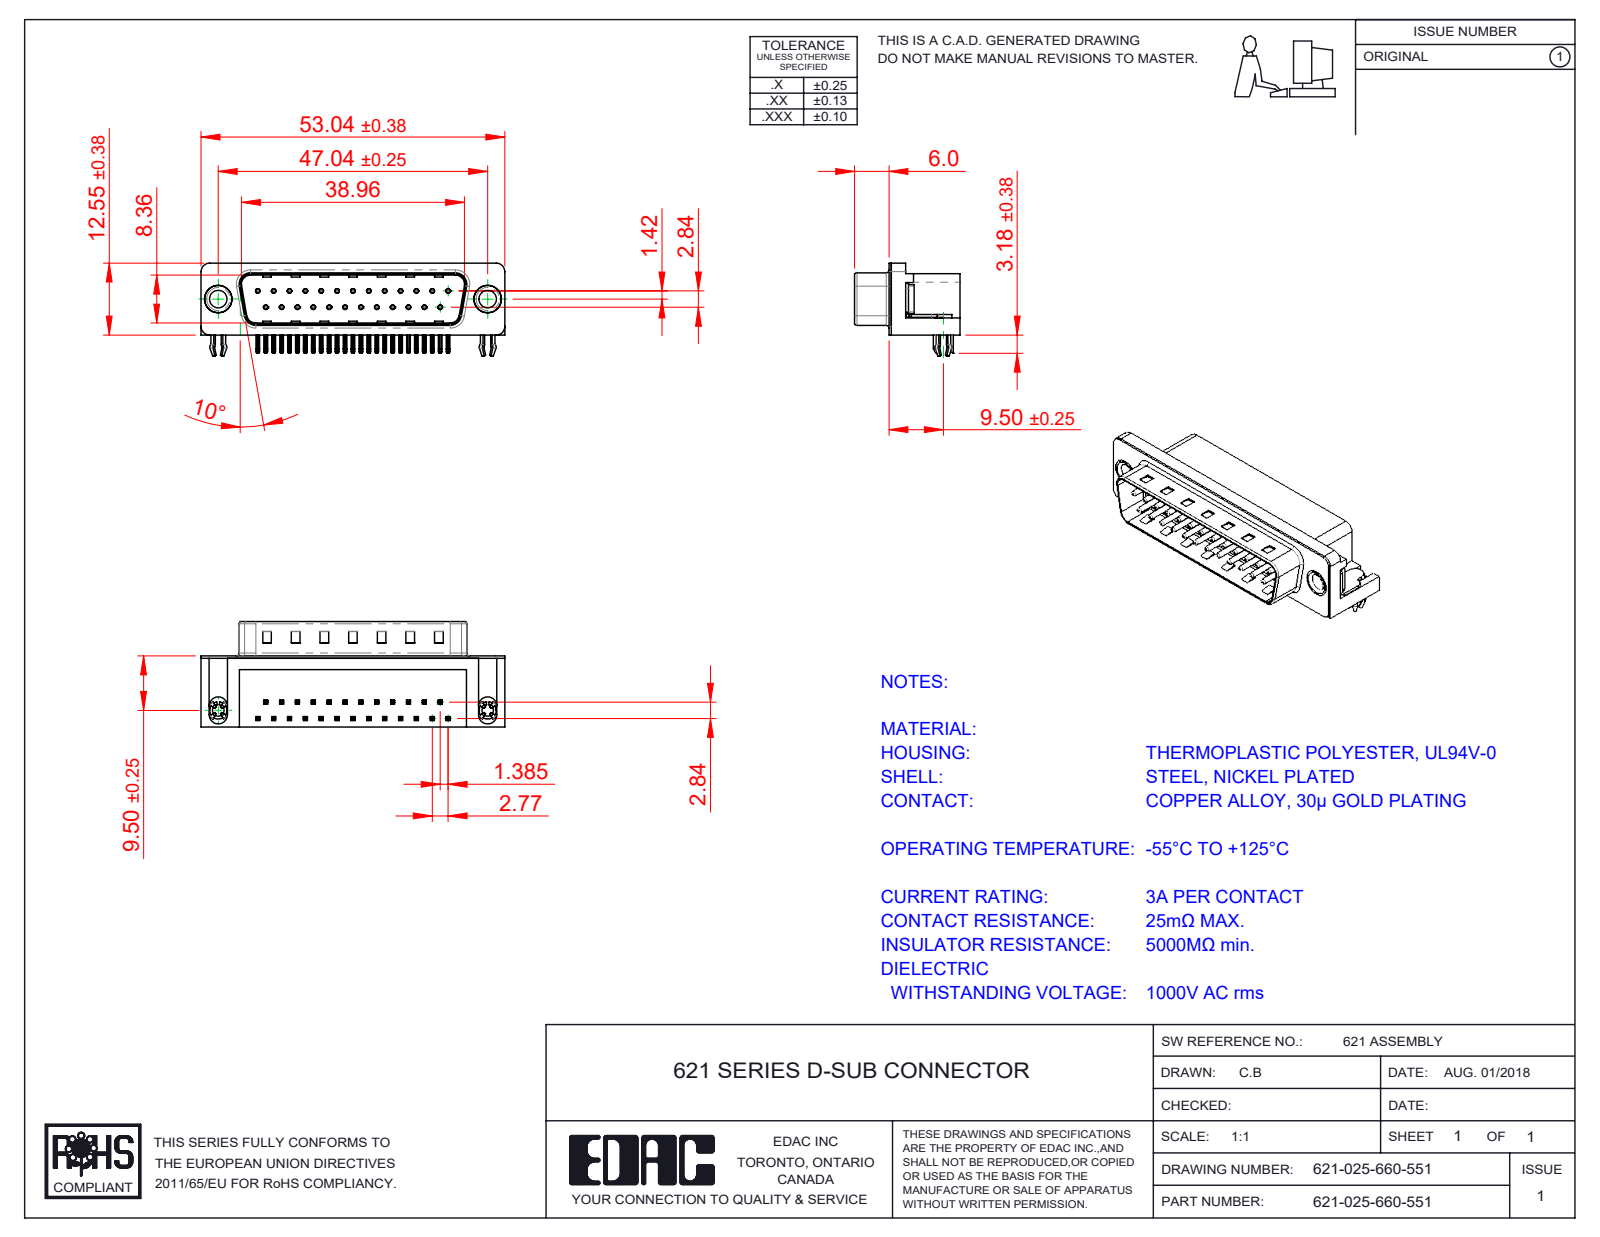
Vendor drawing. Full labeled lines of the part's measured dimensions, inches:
Part name (STEP PRODUCT): 621 Housing_25 Socket; 621 Contact Bottom; 621 Contact Top; 621 Shell_25 Socket (+3 more)
STEP written by: SolidWorks 2016 (CONFIG_CONTROL_DESIGN)
Units: inches
Bodies: 31 solids, 2253 faces (1405 planar, 653 cylindrical, 195 other)
Overall size (bounding box): 2.088 × 0.724 × 0.619
Volume: 0.387 in³ · Surface area: 11.99 in²
Round holes (diameter × count): ⌀0.014 ×25, ⌀0.031 ×25, ⌀0.089 ×2, ⌀0.12 ×2, ⌀0.157 ×2, ⌀0.189 ×2, ⌀0.197 ×2
Round bosses / shafts (diameter × count): ⌀0.03 ×25, ⌀0.193 ×2, ⌀0.187 ×2, ⌀0.152 ×2, ⌀0.128 ×2
Partial cylindrical surfaces — rounded edges, fillets, slot ends (radius × count): R0.01 ×108, R0.005 ×50, R0.039 ×16, R0.02 ×9, R0.063 ×8, R0.059 ×7, R0.035 ×4, R0.079 ×4
Main face-to-face distances: 0.016, 0.472, 0.407, 0.083, 0.345, 0.412, 0.067, 0.428, 0.488, 0.354
Hole centre spacings: 0.124, 0.109, 0.218, 0.327, 0.436, 0.545, 0.654, 0.198
